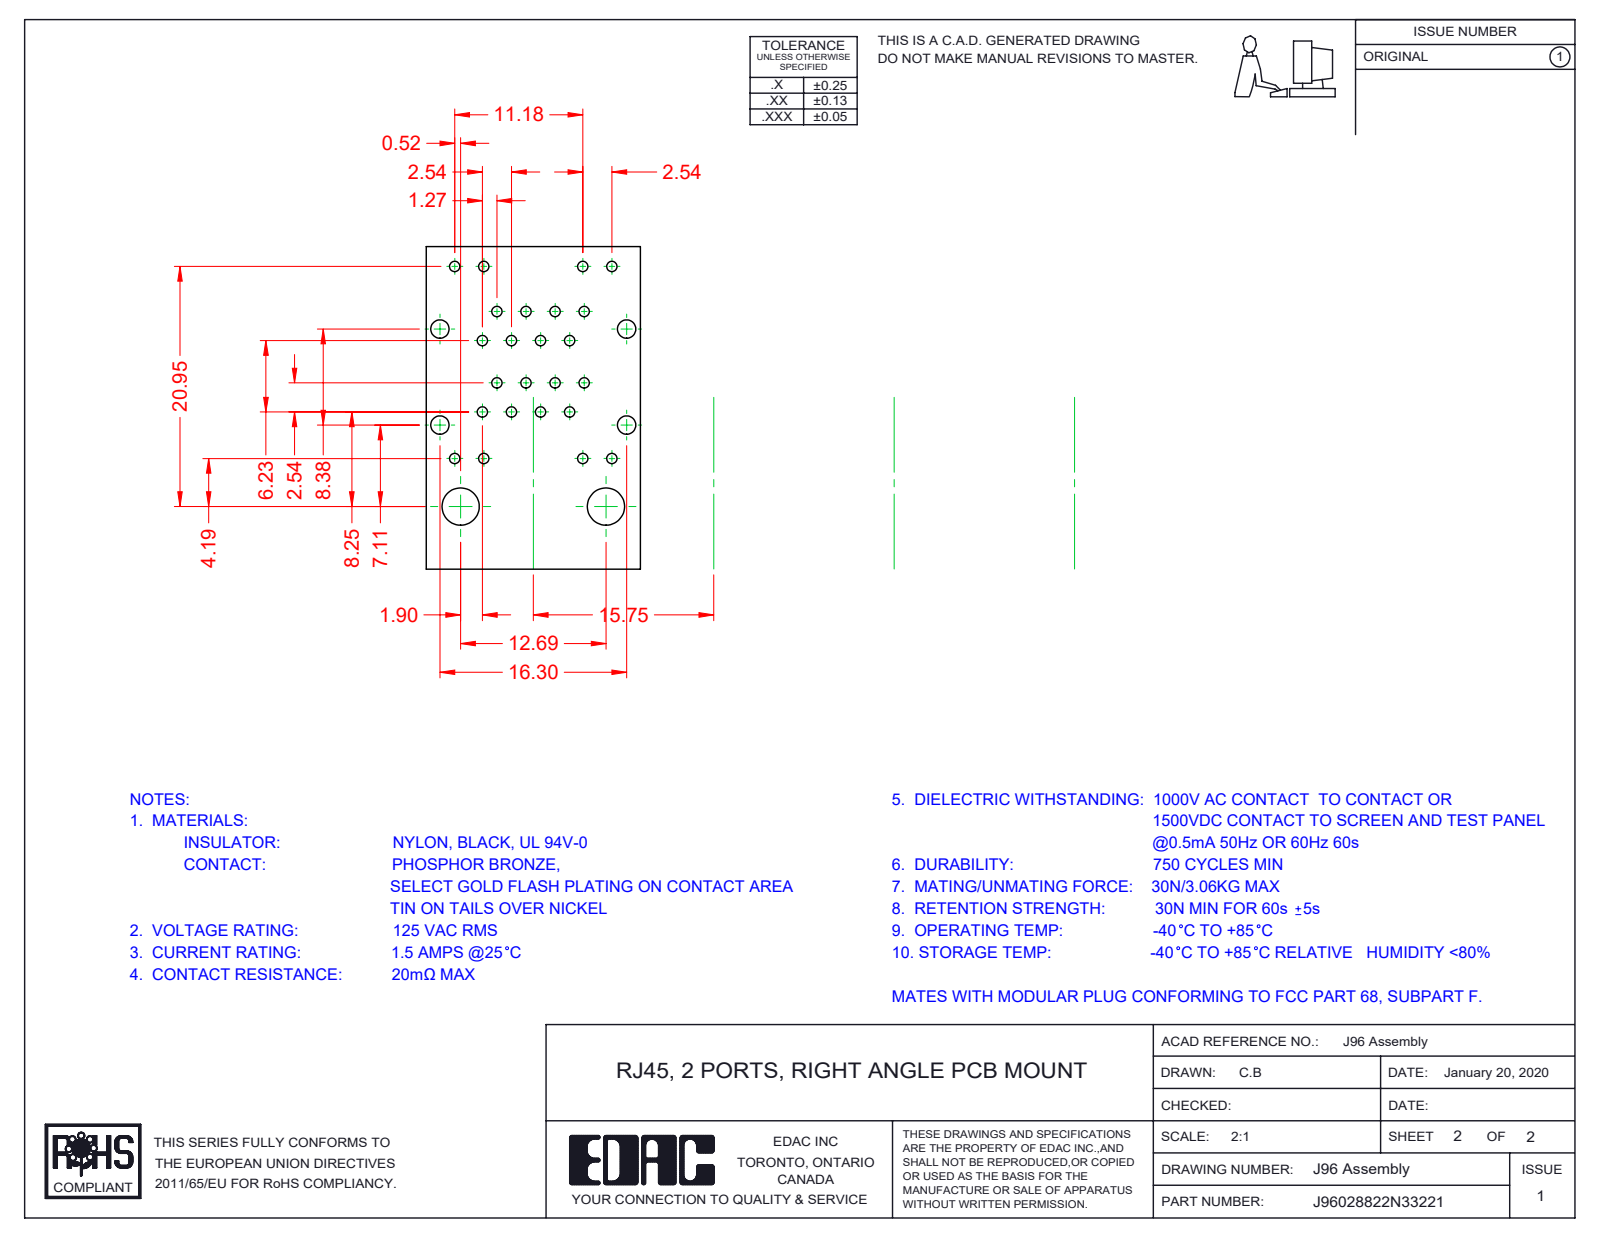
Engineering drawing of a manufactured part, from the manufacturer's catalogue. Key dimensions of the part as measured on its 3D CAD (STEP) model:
Part name (STEP PRODUCT): 96 LED RH Lower_3-Green; 96 LED LH Upper_3-Green; 96 Insulator Insert; 96 LED RH Upper_3-Green (+8 more)
STEP written by: SolidWorks 2016 (CONFIG_CONTROL_DESIGN)
Units: millimetres
Bodies: 27 solids, 2417 faces (1865 planar, 446 cylindrical, 106 other)
Overall size (bounding box): 31.38 × 28.68 × 16.8
Volume: 6 849 mm³ · Surface area: 19 094 mm²
Partial cylindrical surfaces — rounded edges, fillets, slot ends (radius × count): R0.25 ×48, R0.15 ×32, R0.35 ×24, R0.5 ×16, R1 ×16, R0.2 ×14, R0.7 ×9, R2 ×5
Main face-to-face distances: 16.3, 16.1, 1.75, 16.5, 14.75, 1.55, 14.55, 0.53, 1.48, 11.2
